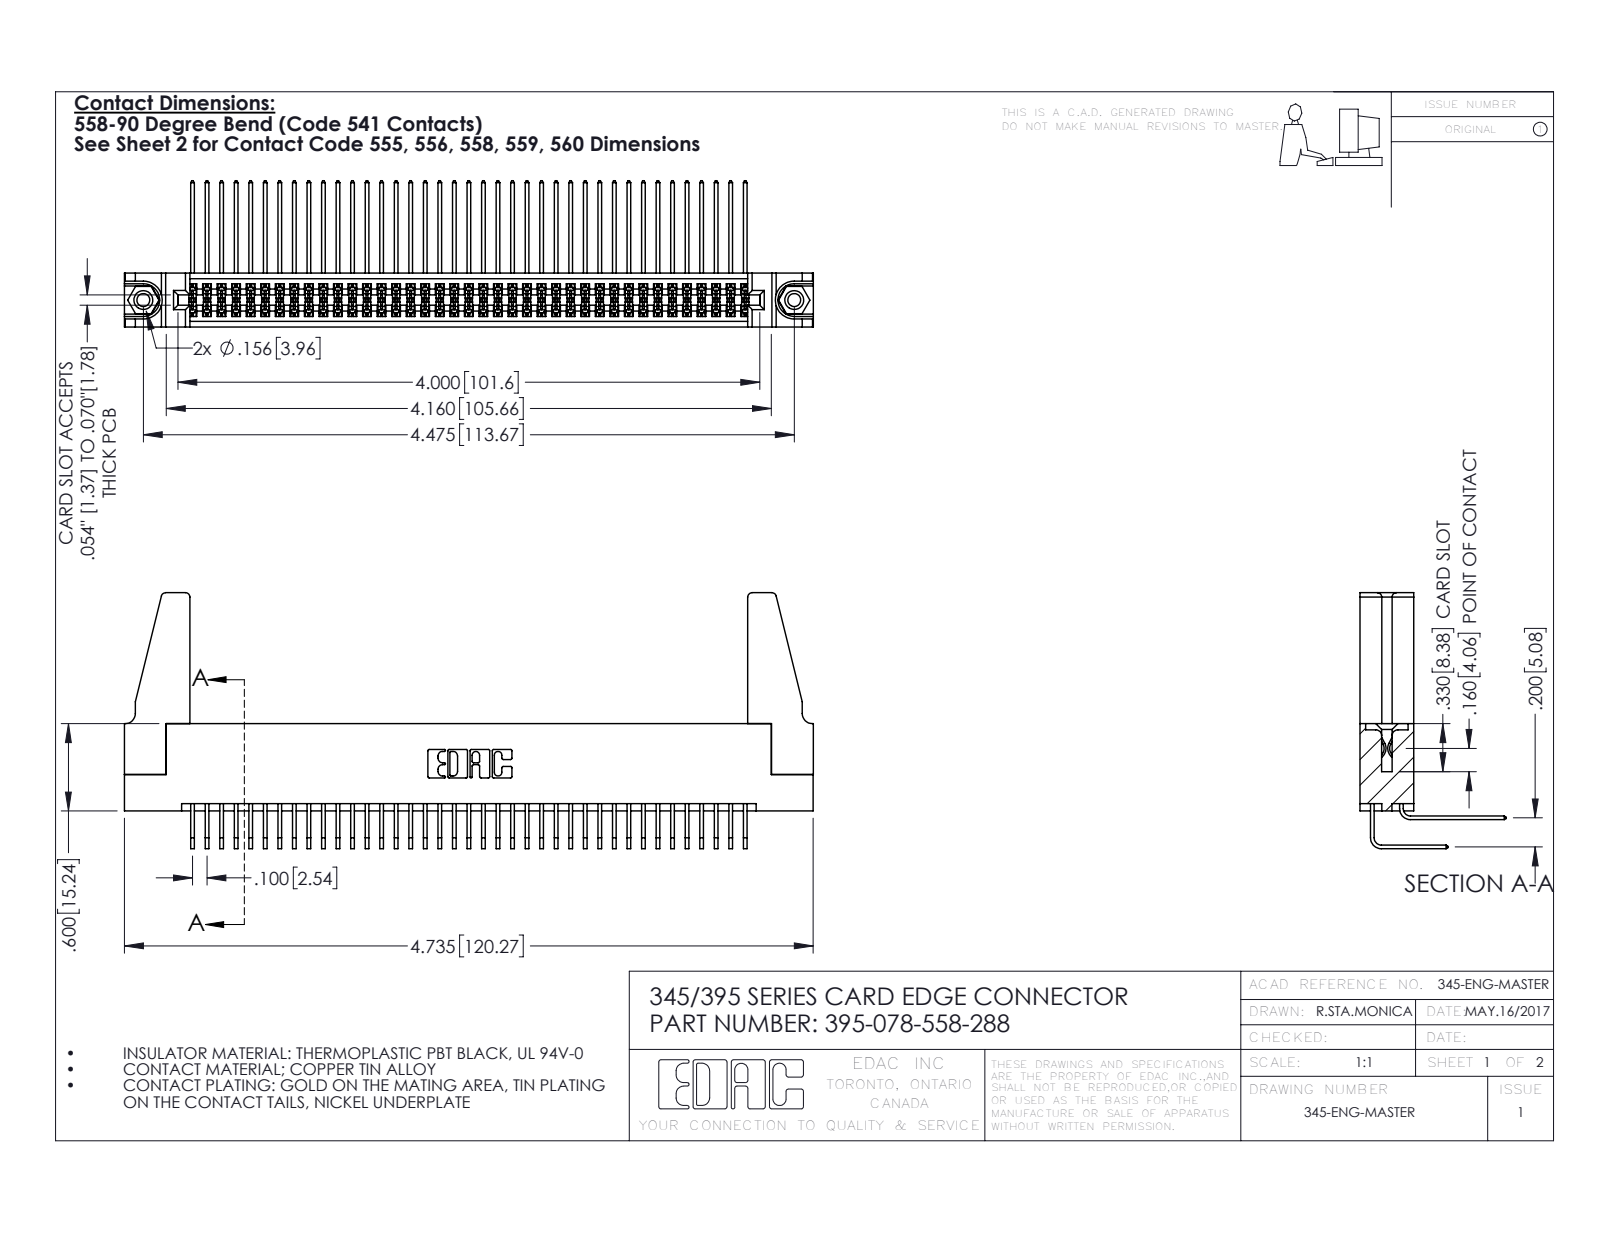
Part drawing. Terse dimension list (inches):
name: 345-220-078_345-220-088; 345-250-001_345-250-001-102; 345 Part_Flush Mounting Lugs - 0.156 Dia-TH; 345-292-001_558 559 Tail - 1 (+2 more)
written by: SolidWorks 2016 (CONFIG_CONTROL_DESIGN)
unit: in
bodies: 83 solids, 4306 faces (2882 planar, 1408 cylindrical, 16 other)
size: 4.736 × 1.759 × 1.005
volume: 0.937 in³; area: 35.77 in²
holes: 2× ⌀0.089, 2× ⌀0.125, 2× ⌀0.156, 1× ⌀0.064
bosses: 2× ⌀0.155
rounds: 118× R0.006, 22× R0.01, 8× R0.03, 6× R0.007, 6× R0.031, 3× R0.026, 2× R0.014, 2× R0.019
face distances: 0.072, 0.298, 0.2, 0.37, 0.098, 0.272, 0.025, 0.225, 0.285, 0.025
hole spacings: 0.27, 4.239, 4.475
